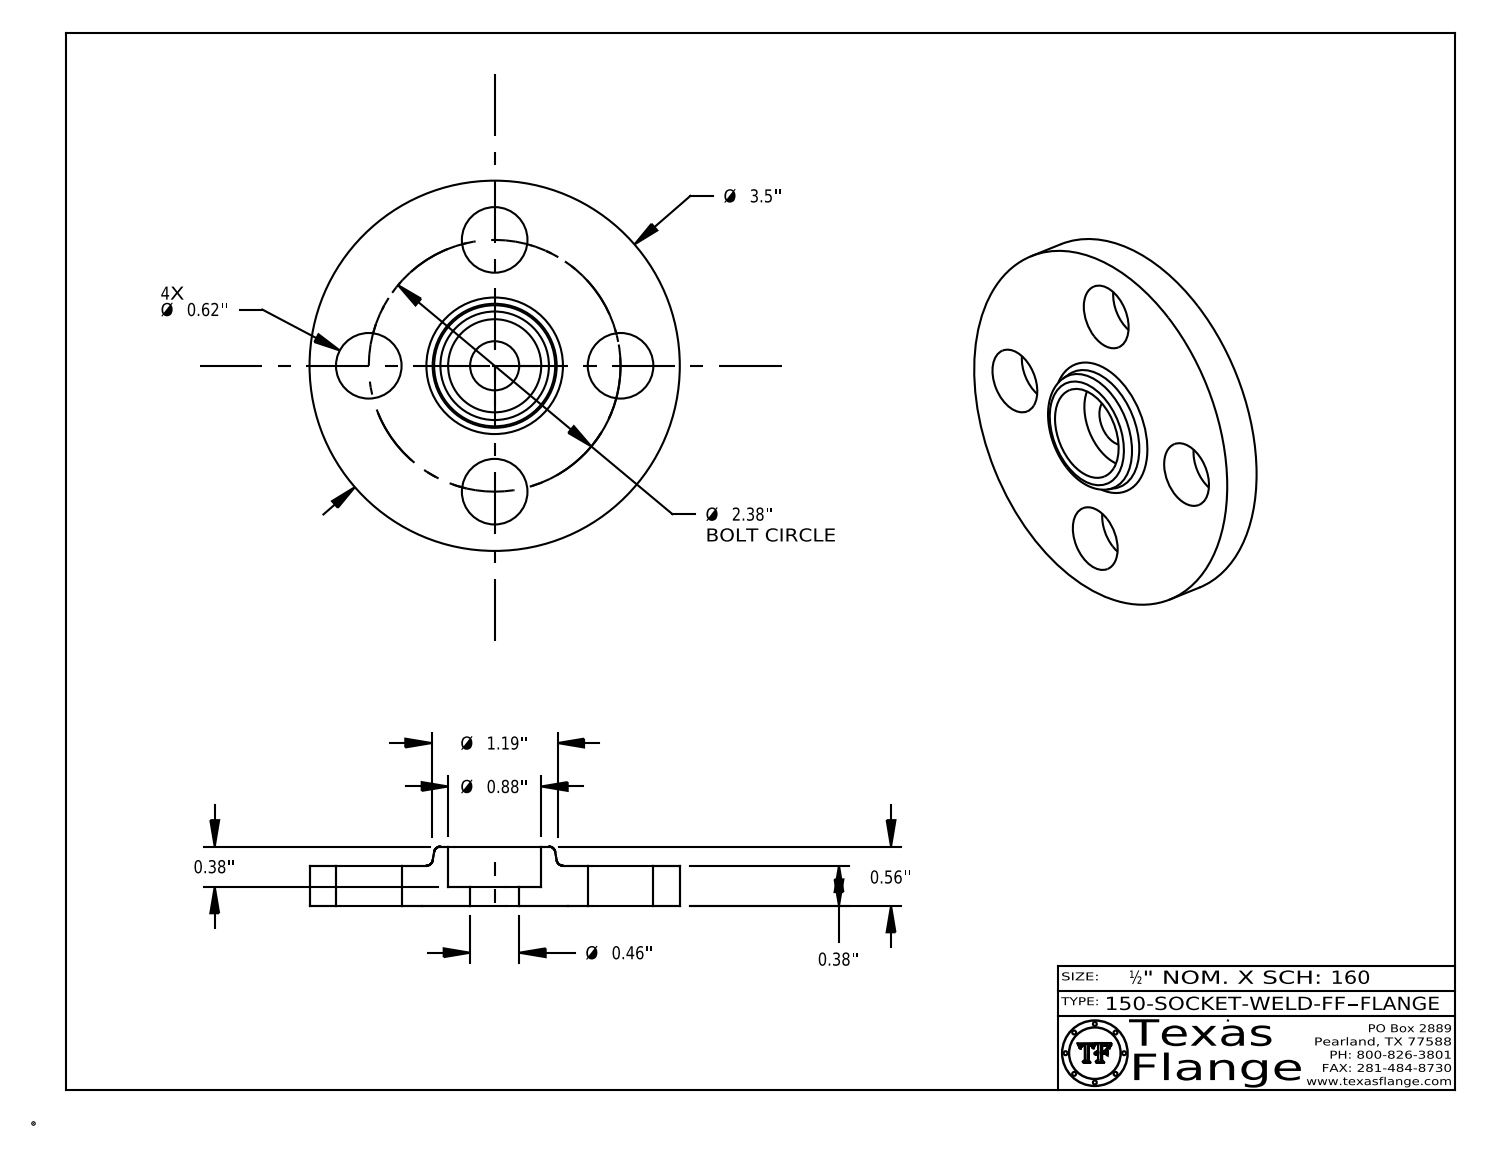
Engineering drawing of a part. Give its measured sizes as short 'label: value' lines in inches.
name: 150-SOCKET-WELD-FF
written by: CATIA V5 STEP AP214 (AUTOMOTIVE_DESIGN)
unit: in
bodies: 1 solid, 410 faces (370 planar, 34 cylindrical, 6 other)
size: 3.5 × 3.5 × 0.56
volume: 3.124 in³; area: 25.46 in²
holes: 4× ⌀0.62, 1× ⌀0.464, 1× ⌀0.495, 1× ⌀0.88
bosses: 8× ⌀0.03, 1× ⌀3.5, 1× ⌀0.39
face distances: 0.38, 0.18, 0.2, 0.56, 0.365, 0.185, 0.015, 0.195, 0.148, 0.145
hole spacings: 1.19, 1.683, 0.911, 2.199, 2.38, 1.19
